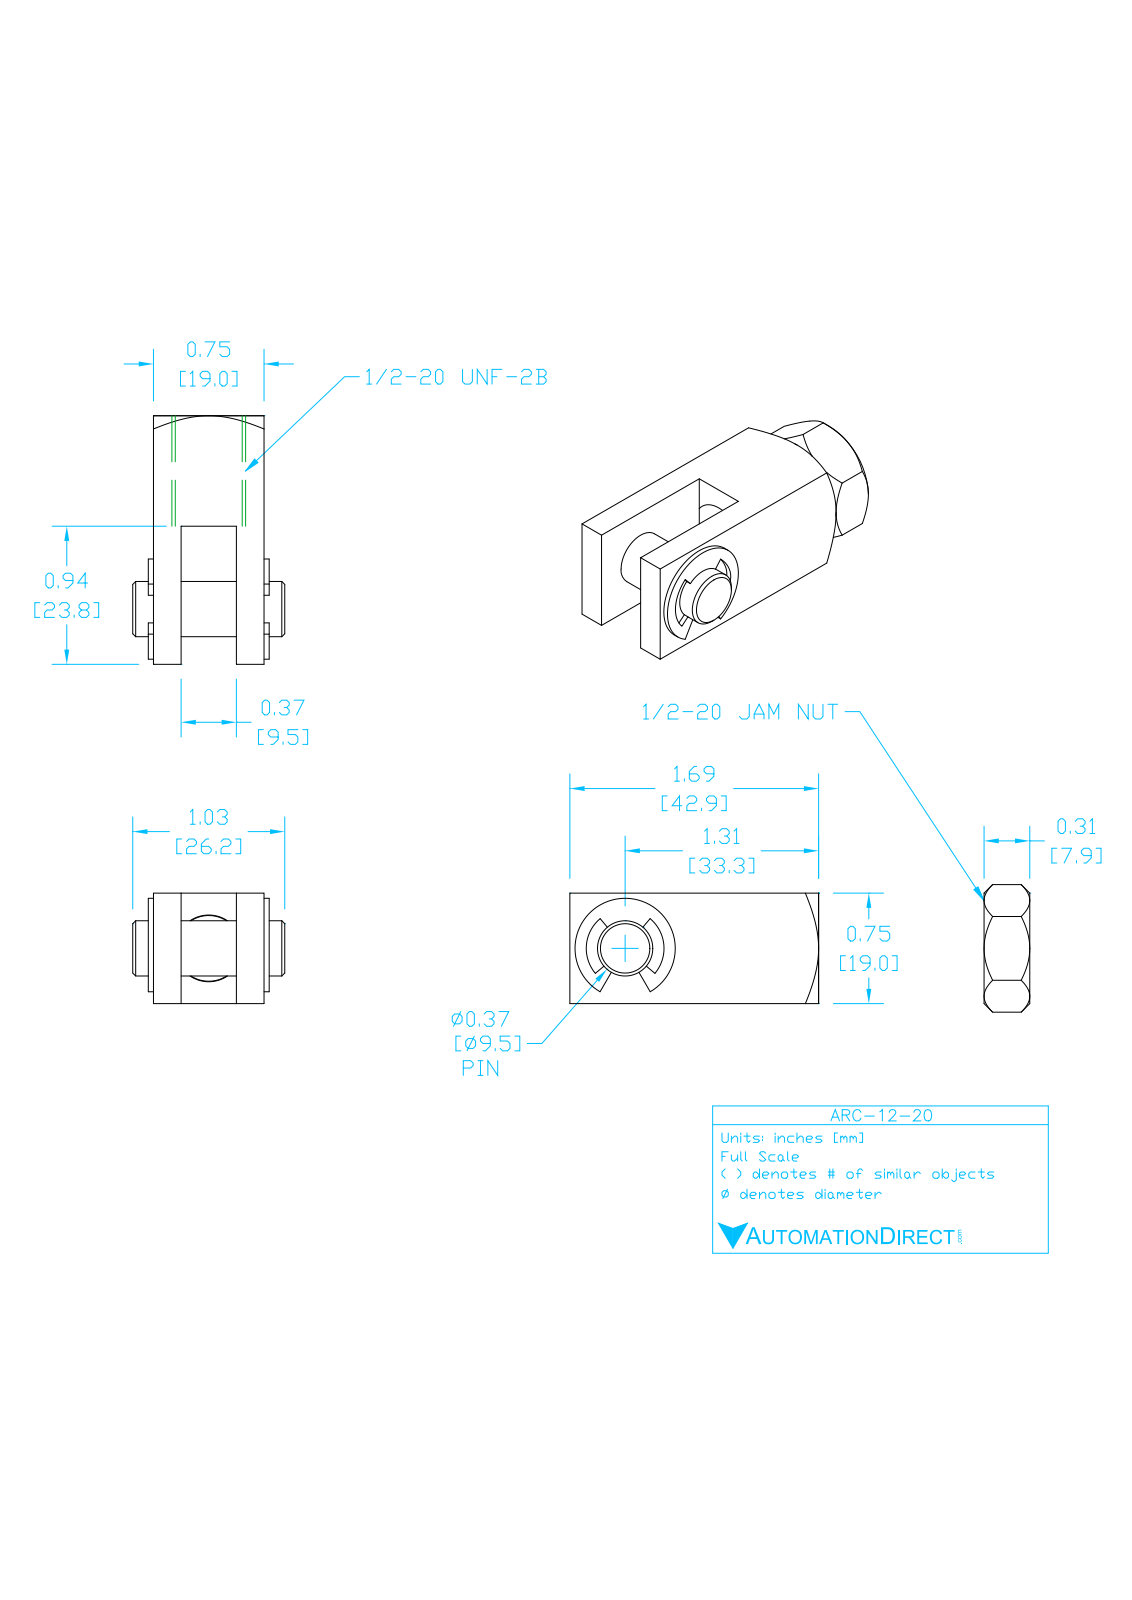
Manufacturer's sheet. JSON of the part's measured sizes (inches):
{"part_name": "ARC-12-20", "step_written_by": "SolidWorks 2017 (AUTOMOTIVE_DESIGN)", "units": "inches", "bodies": {"solids": 5, "faces": 139, "planar": 43, "cylindrical": 62, "other": 34}, "overall_size": [2, 1.031, 0.866], "volume_in3": 0.745, "surface_area_in2": 12.17, "round_holes": [[0.38, 1], [0.446, 1]], "round_bosses_or_shafts": [[0.377, 1], [0.304, 1]], "partial_cylinders_radius": [[0.031, 6], [0.035, 4], [0.053, 2], [0.152, 1], [0.264, 1], [0.375, 1]], "face_to_face_distances": [0.75, 0.18, 0.569, 0.796, 0.389, 0.037, 0.041, 0.222, 0.611, 0.791]}
